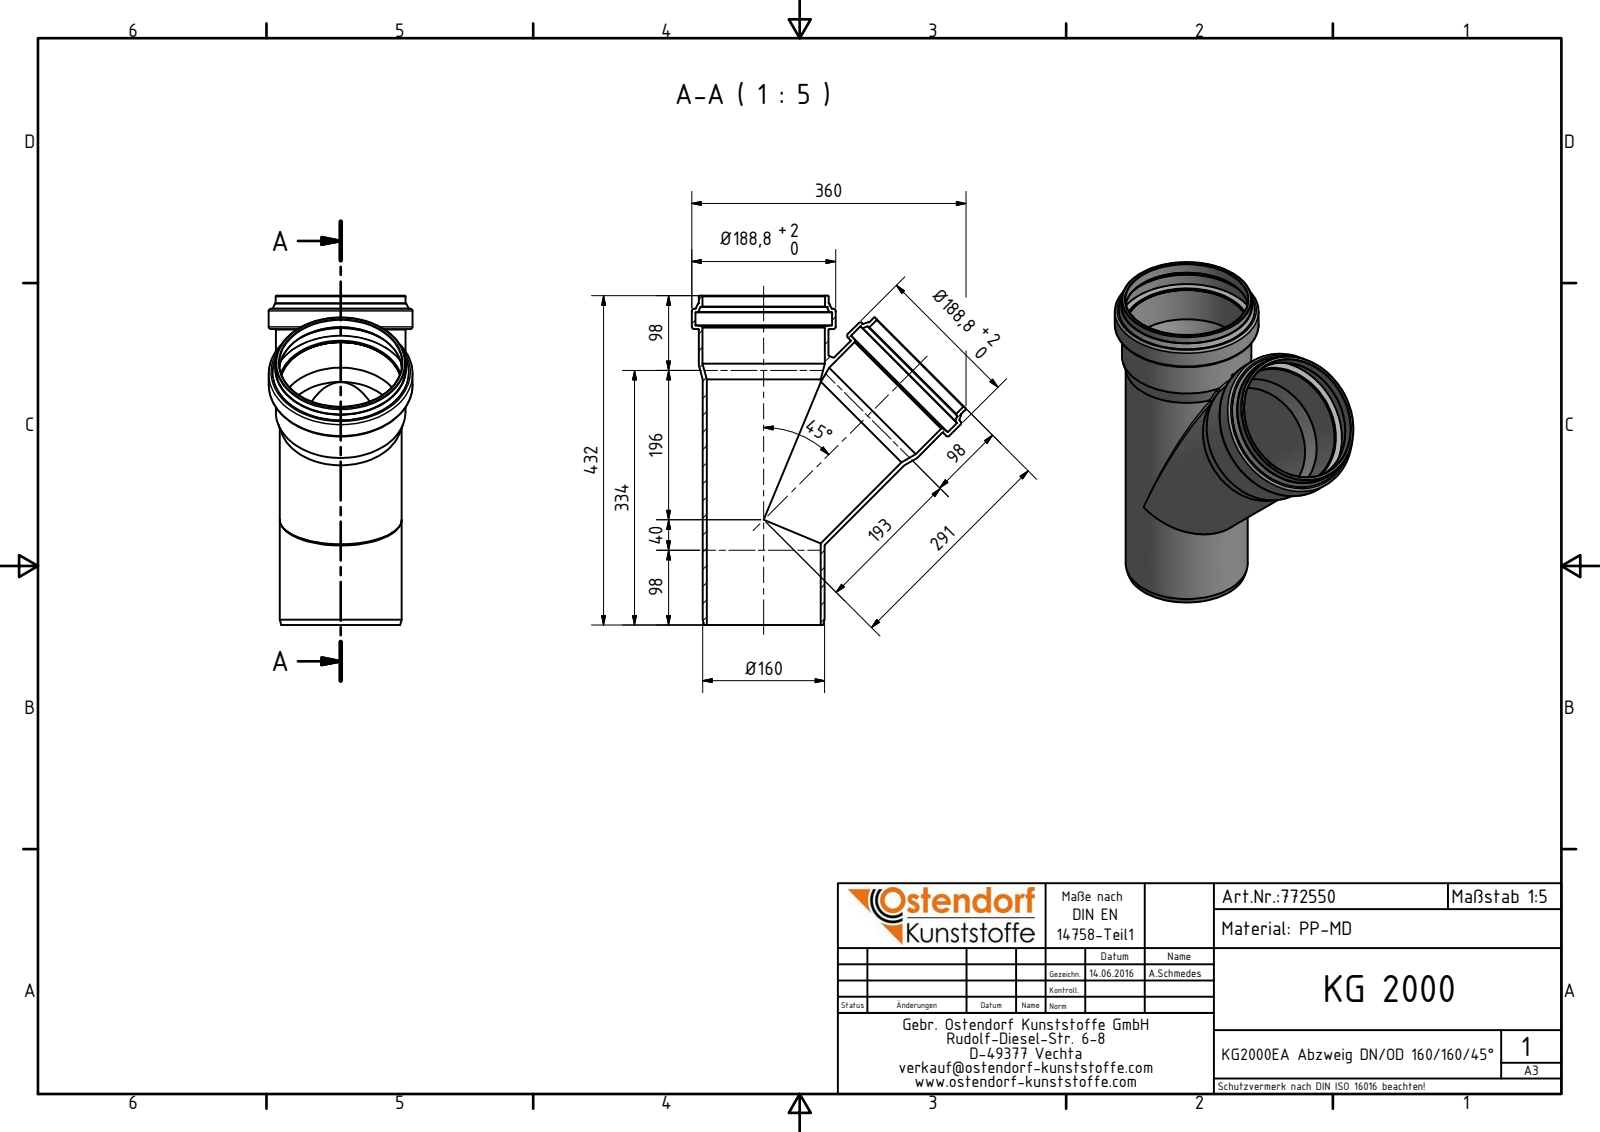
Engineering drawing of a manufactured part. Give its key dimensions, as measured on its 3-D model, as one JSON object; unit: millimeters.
{"part_name": "772550 KG2000EA Abzweig DN_OD 160_160_45°", "step_written_by": "Autodesk Inventor 2016 (AUTOMOTIVE_DESIGN)", "units": "millimeters", "bodies": {"solids": 1, "faces": 85, "planar": 14, "cylindrical": 19, "other": 52}, "overall_size": [432, 360, 188.8], "volume_mm3": 1561000, "surface_area_mm2": 621368, "round_holes": [[161, 3], [149.54, 2], [160.7, 2], [179.4, 2]], "round_bosses_or_shafts": [[188.8, 2], [170.4, 2], [170.1, 2], [160.1, 2]], "face_to_face_distances": [26.7, 388.3, 43.69, 432, 43.7, 415, 17, 16.99, 33.61, 6.91]}
